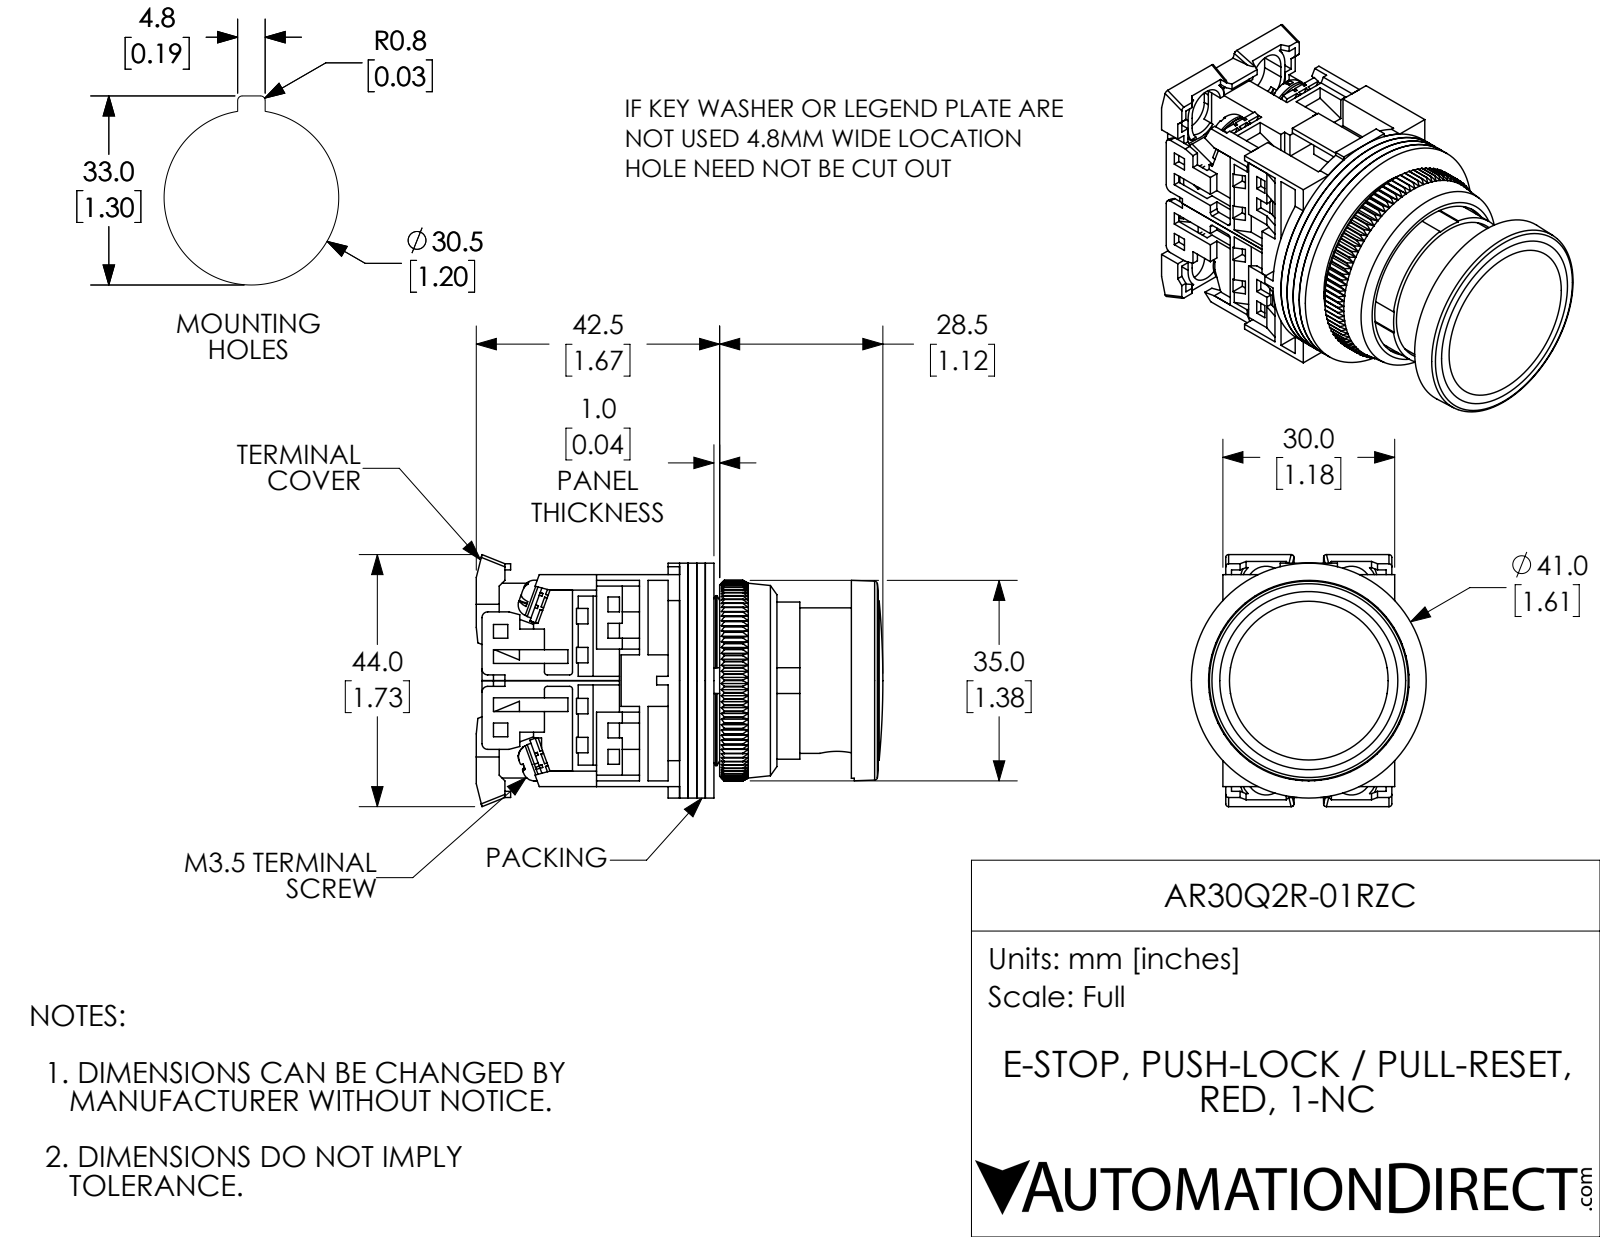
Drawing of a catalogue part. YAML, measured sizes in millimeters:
part_name: "AR30Q2R-01RZC"
step_written_by: "SolidWorks 2017 (AUTOMOTIVE_DESIGN)"
units: millimeters
bodies: {solids: 25, faces: 1785, planar: 1232, cylindrical: 329, other: 224}
overall_size: [71, 44, 41]
volume: 51930
surface_area: 44940
round_holes:
  - {diameter: 3.5, count: 4}
  - {diameter: 3.6, count: 4}
  - {diameter: 2.6, count: 1}
  - {diameter: 2.9, count: 1}
  - {diameter: 3, count: 1}
  - {diameter: 6, count: 1}
  - {diameter: 13, count: 1}
  - {diameter: 16, count: 1}
  - {diameter: 20.4, count: 1}
  - {diameter: 23.8, count: 1}
  - {diameter: 26, count: 1}
  - {diameter: 28.5, count: 1}
round_bosses_or_shafts:
  - {diameter: 6.6, count: 4}
  - {diameter: 3.5, count: 4}
  - {diameter: 41, count: 1}
  - {diameter: 30, count: 1}
  - {diameter: 27.5, count: 1}
  - {diameter: 25.4, count: 1}
  - {diameter: 20, count: 1}
  - {diameter: 18, count: 1}
partial_cylinders:
  - {radius: 1.5, count: 21}
  - {radius: 0.5, count: 12}
  - {radius: 1, count: 4}
  - {radius: 3.5, count: 4}
  - {radius: 4.5, count: 4}
  - {radius: 3, count: 2}
  - {radius: 7, count: 1}
  - {radius: 10.1, count: 1}
face_to_face_distances: [1.5, 3, 1, 4.5, 36, 2, 17.5, 34.5, 3.5, 0.5]
hole_center_spacings: [14.7, 15.5]
